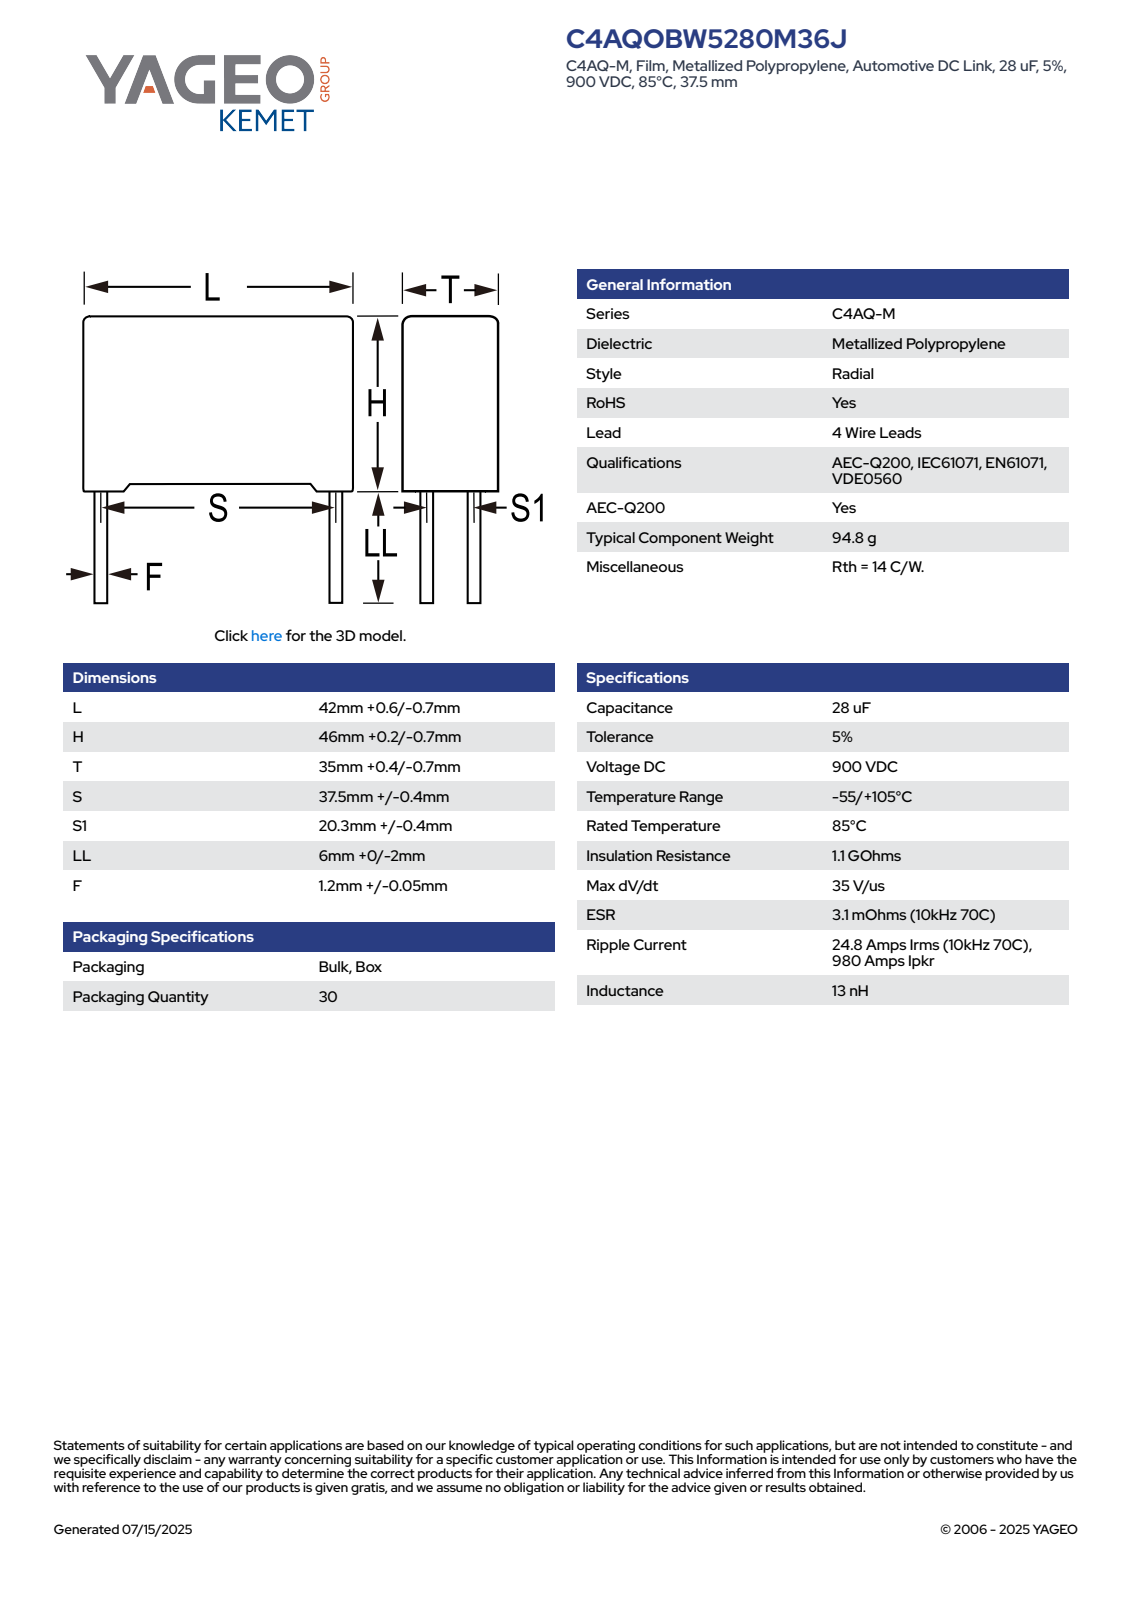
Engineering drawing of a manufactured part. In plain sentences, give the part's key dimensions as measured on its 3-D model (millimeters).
The part is named "CFP_RB4_42X46X35_L42.6H46.2T35.4S37.5S120.3LL6F1.25". Its 3-D file was written by "SolidWorks 2014 (AUTOMOTIVE_DESIGN)". It is 4 solids with 91 faces: 83 planar, 8 cylindrical and 0 other. Overall it measures 52.2 by 42.6 by 35.41 millimeters. Its volume is 67 930 cubic millimeters and its surface area 10 488 square millimeters. Round bosses or shafts: 4 of diameter 1.25. The main face-to-face distances are 35.4, 42.6, 44.84, 1.36, 46.2, 2.18, 40.42, 35.41, 38.24, 33.22.
